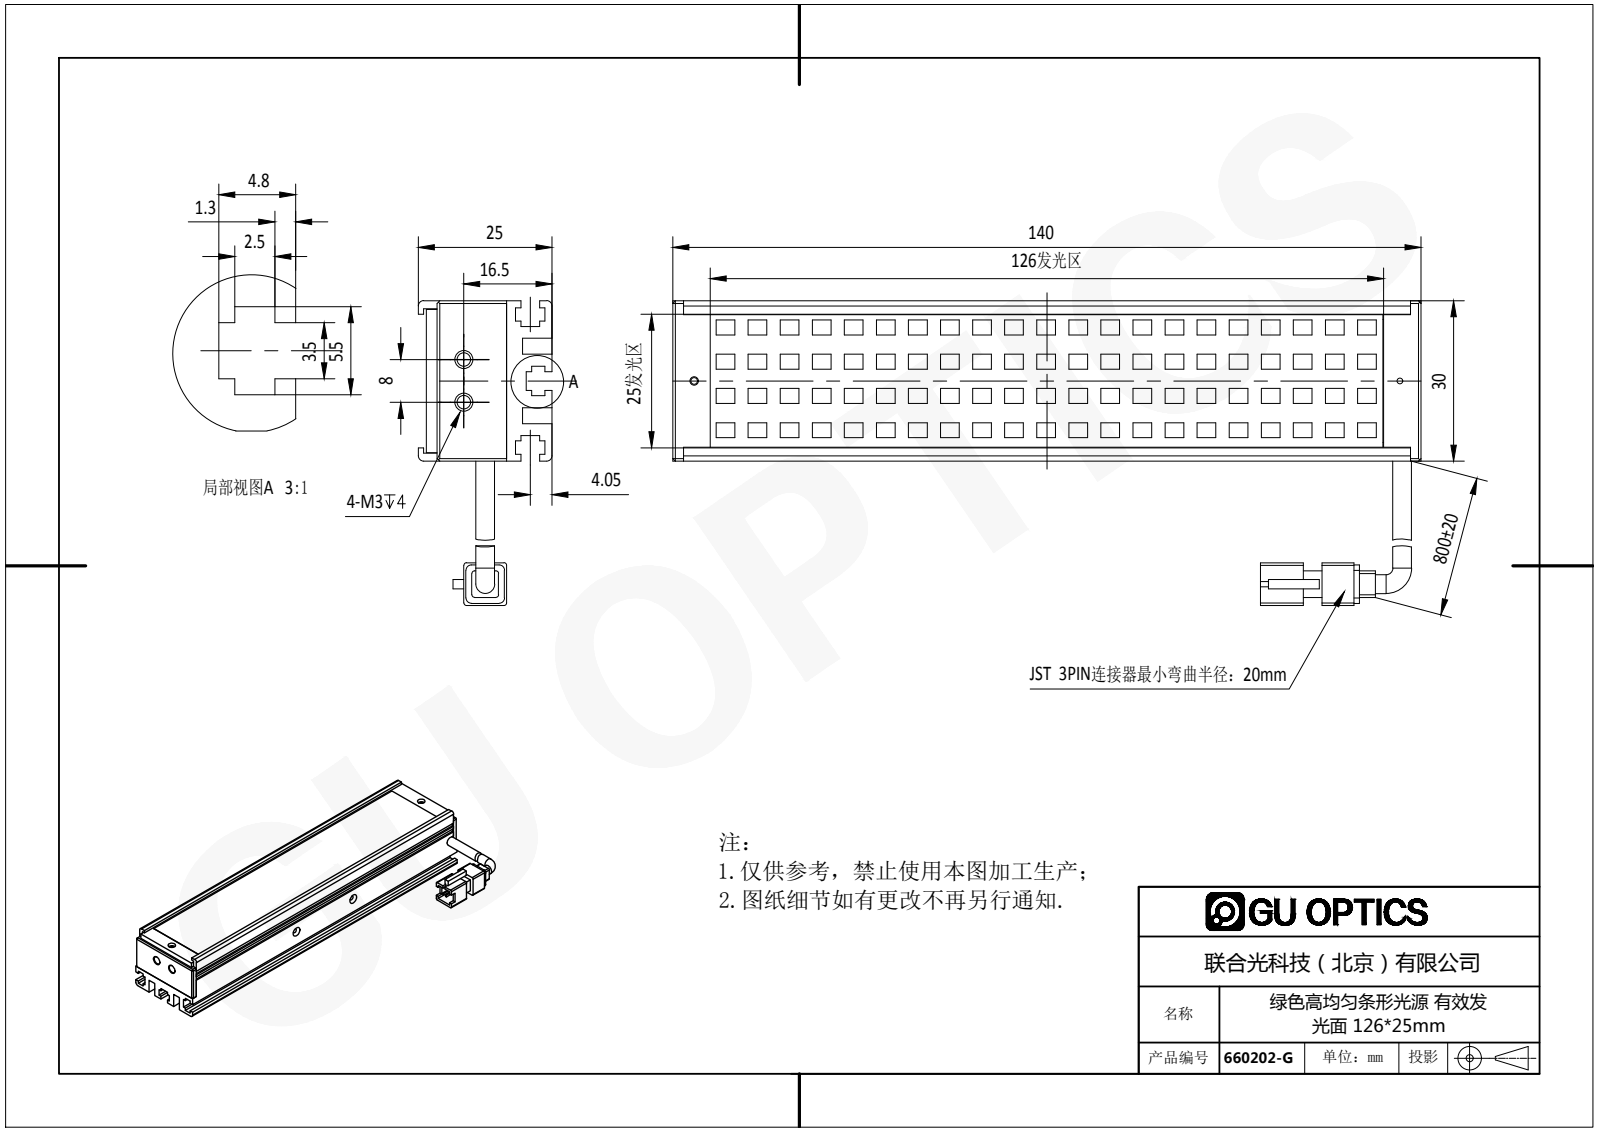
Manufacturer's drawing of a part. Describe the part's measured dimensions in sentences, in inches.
The part is named "660202-G". Its 3-D file was written by "SolidWorks 2016 (AUTOMOTIVE_DESIGN)". It is 6 solids with 864 faces: 678 planar, 83 cylindrical and 103 other. Overall it measures 5.512 by 2.244 by 0.984 inches. Its volume is 3.043 cubic inches and its surface area 78.16 square inches. Round holes: 5 of diameter 0.063, 2 of diameter 0.059, 2 of diameter 0.067, 2 of diameter 0.098, 2 of diameter 0.11, 2 of diameter 0.118, 1 of diameter 0.043, 1 of diameter 0.049, 1 of diameter 0.079. Round bosses or shafts: 2 of diameter 0.138. Partial cylindrical surfaces (rounded edges, fillets, slot ends): 12 of radius 0.039, 8 of radius 0.02, 1 of radius 0.065. The main face-to-face distances are 0.039, 0.512, 0.079, 0.098, 0.118, 0.374, 1.083, 0.177, 0.335, 0.846. The hole center spacings are 5.197, 0.276, 2.008, 2.025, 3.189, 3.2, 5.204, 0.315.
